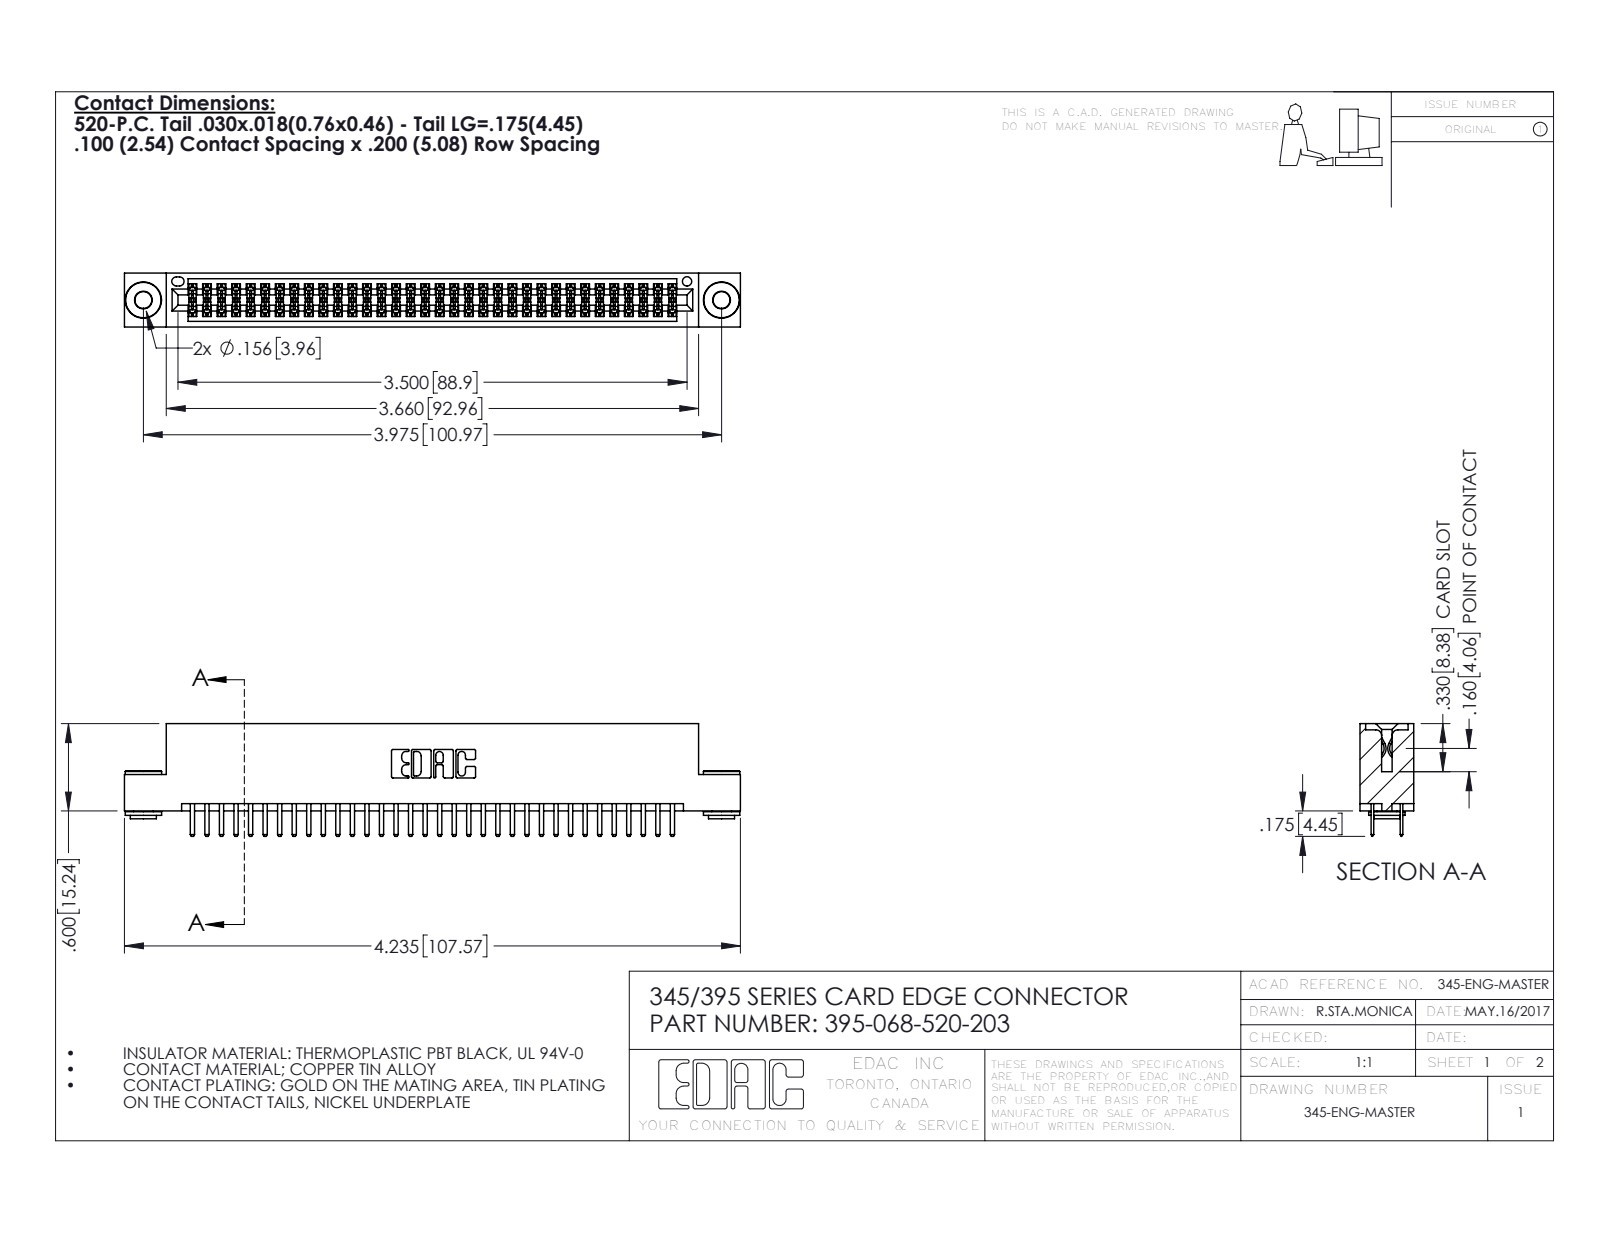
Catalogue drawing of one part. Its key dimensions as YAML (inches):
part_name: "345-250-002_345-250-002-102; 345-292-001_345-293-120; 395-068-520-203; 345 Part_Flush Mounting Lugs - 0.156 Dia-TH"
step_written_by: "SolidWorks 2016 (CONFIG_CONTROL_DESIGN)"
units: inches
bodies: {solids: 71, faces: 3836, planar: 2470, cylindrical: 1358, other: 8}
overall_size: [4.235, 0.775, 0.37]
volume: 0.632
surface_area: 23.73
round_holes:
  - {diameter: 0.116, count: 2}
  - {diameter: 0.156, count: 2}
  - {diameter: 0.064, count: 1}
round_bosses_or_shafts:
  - {diameter: 0.25, count: 2}
  - {diameter: 0.18, count: 2}
  - {diameter: 0.136, count: 2}
partial_cylinders:
  - {radius: 0.006, count: 102}
  - {radius: 0.01, count: 72}
  - {radius: 0.01, count: 22}
  - {radius: 0.007, count: 6}
  - {radius: 0.031, count: 6}
  - {radius: 0.026, count: 3}
  - {radius: 0.014, count: 2}
  - {radius: 0.019, count: 2}
face_to_face_distances: [0.072, 0.298, 0.2, 0.37, 0.025, 0.098, 0.272, 0.225, 0.022, 0.072]
hole_center_spacings: [0.27, 3.74, 3.975]
